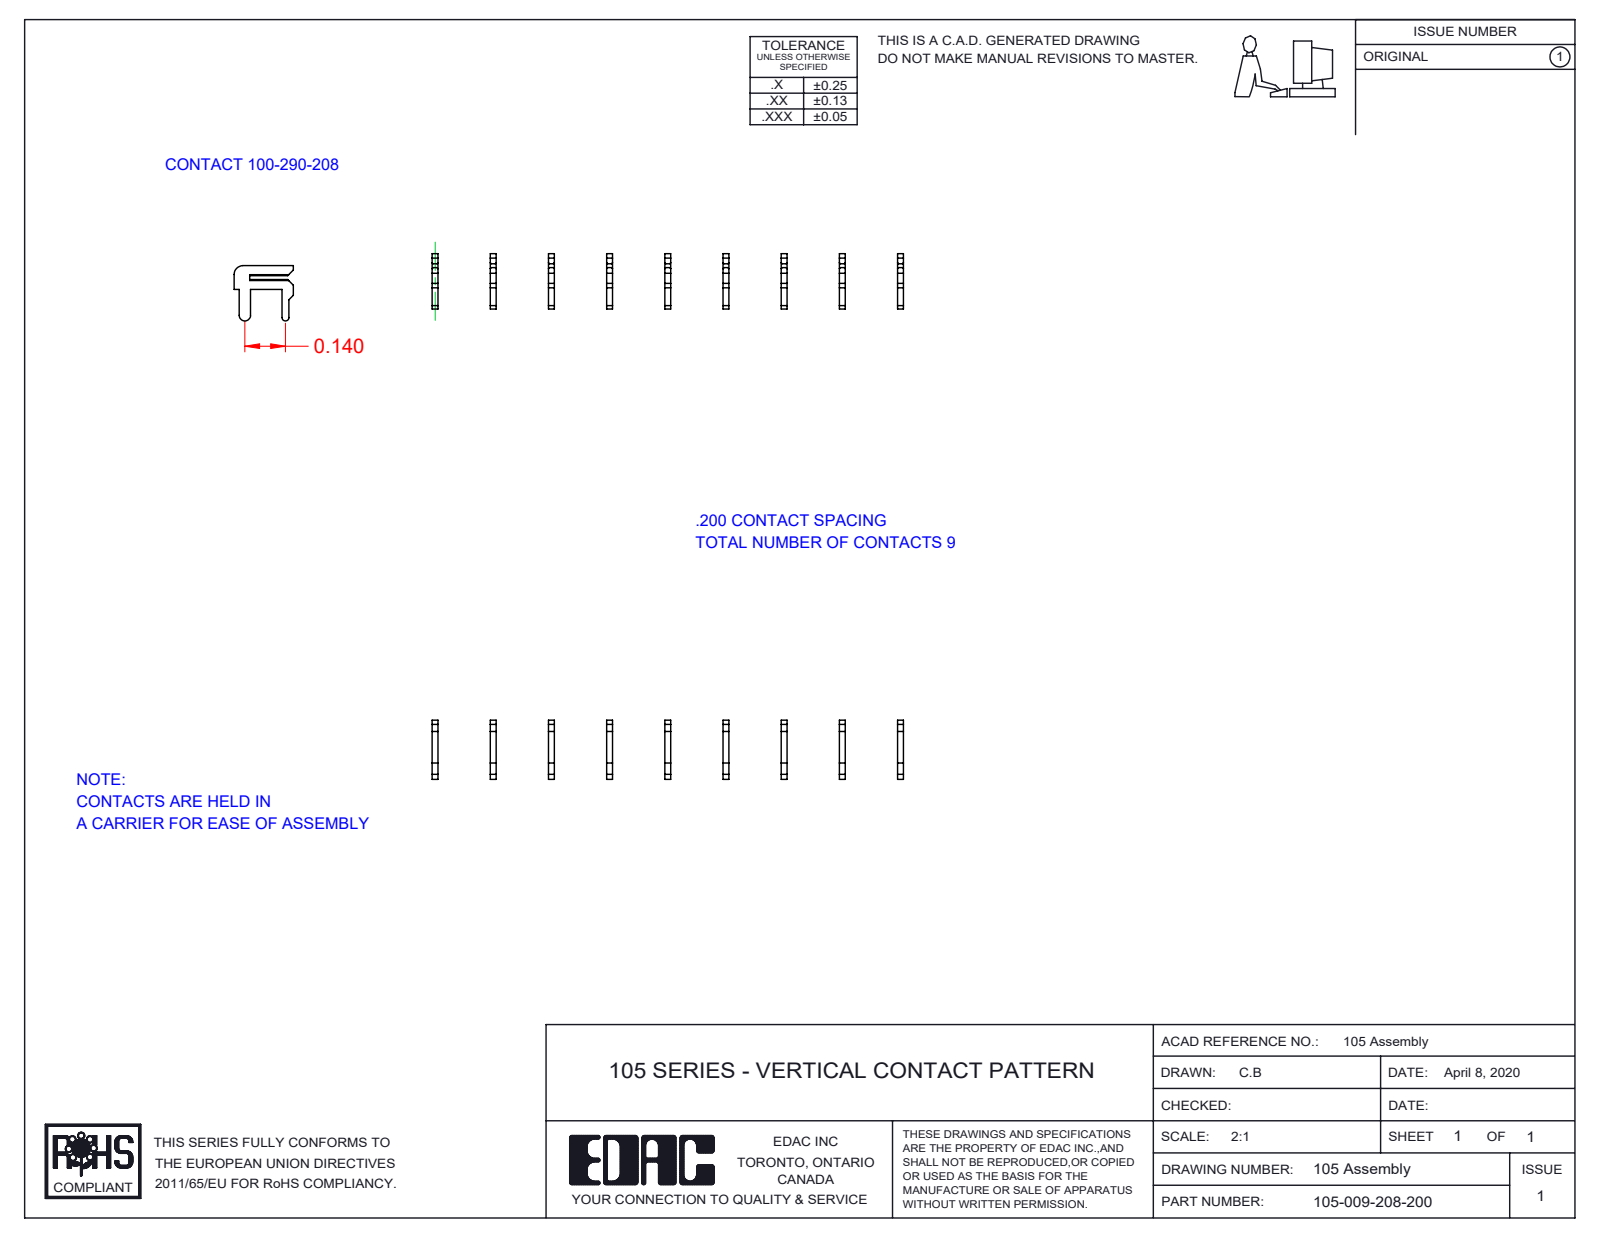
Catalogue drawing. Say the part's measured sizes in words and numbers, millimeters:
The part is named "100-290-001_100-290-208; 105-009-208-200". Its 3-D file was written by "SolidWorks 2016 (CONFIG_CONTROL_DESIGN)". It is 9 solids with 225 faces: 198 planar, 27 cylindrical and 0 other. Overall it measures 41.1 by 5.2 by 4.8 millimeters. Its volume is 70 cubic millimeters and its surface area 383 square millimeters. Partial cylindrical surfaces (rounded edges, fillets, slot ends): 1 of radius 0.3, 1 of radius 0.5, 1 of radius 0.8. The main face-to-face distances are 5.1, 10.2, 15.2, 20.3, 0.5, 25.4, 5.6, 4.6, 10.7, 9.7.
